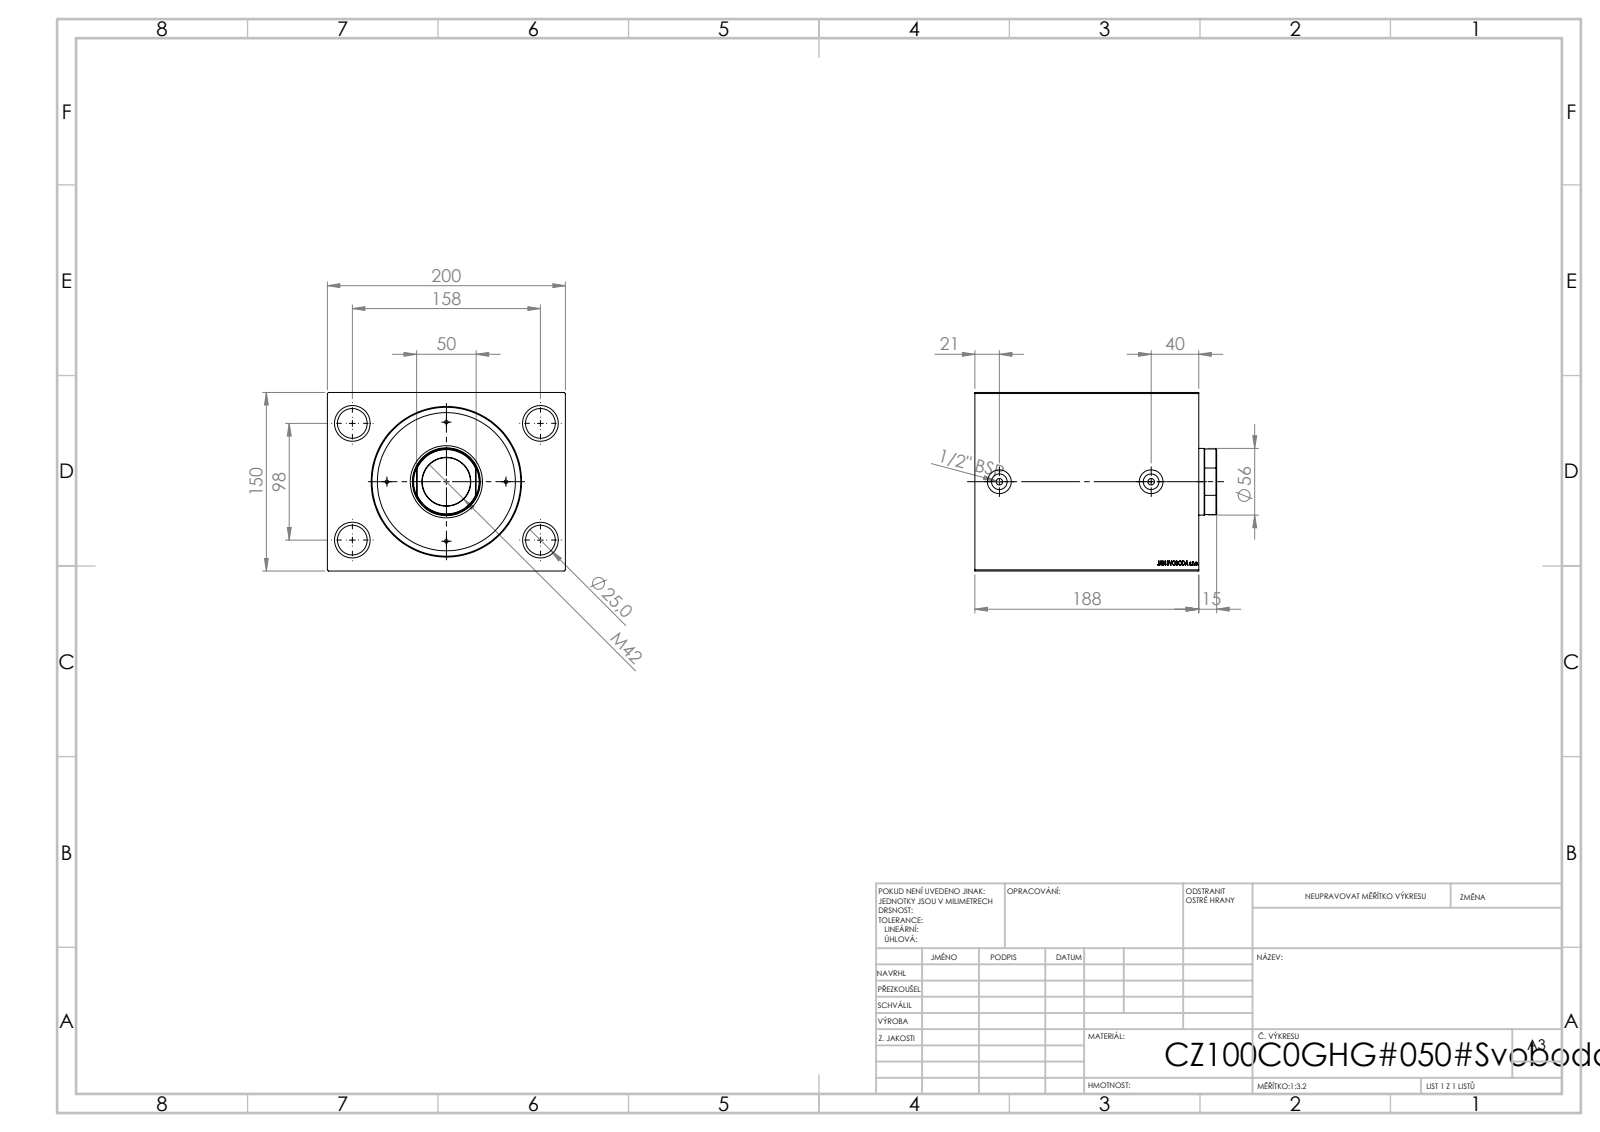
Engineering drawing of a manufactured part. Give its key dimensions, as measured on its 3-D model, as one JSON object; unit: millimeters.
{"step_written_by": "SolidWorks 2019 (CONFIG_CONTROL_DESIGN)", "units": "millimeters", "bodies": {"solids": 1, "faces": 825, "planar": 397, "cylindrical": 46, "other": 382}, "overall_size": [200, 188, 150], "volume_mm3": 3967000, "surface_area_mm2": 298801, "round_holes": [[25, 4], [30, 4], [5.5, 2], [8, 2], [13.16, 2], [20, 2], [36, 1], [100, 1], [125, 1]], "face_to_face_distances": [150, 200, 188, 154.7, 33.3, 15, 139.7, 173, 10.33, 177.67], "hole_center_spacings": [92.96, 98, 158, 185.92, 107.5, 127.5]}
